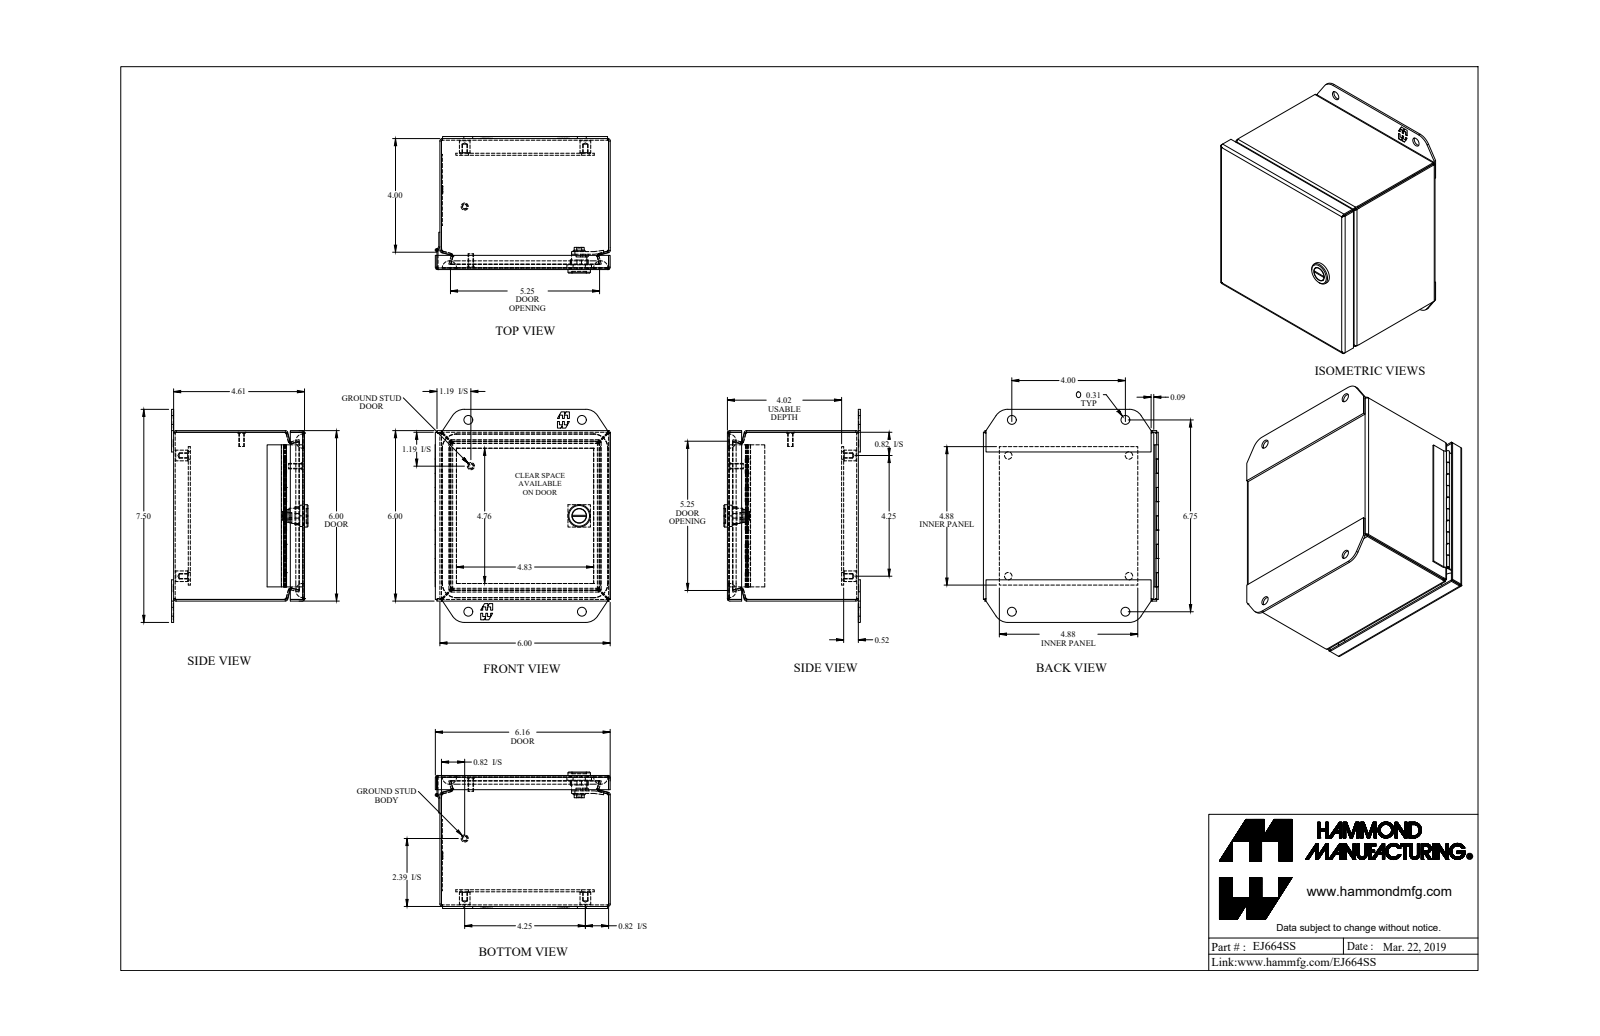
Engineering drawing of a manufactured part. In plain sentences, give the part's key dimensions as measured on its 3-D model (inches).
The part is named "EJ664SS_Default". Its 3-D file was written by "SolidWorks 2019 (CONFIG_CONTROL_DESIGN)". It is 16 solids with 624 faces: 354 planar, 174 cylindrical and 96 other. Overall it measures 7.5 by 6.165 by 4.805 inches. Its volume is 16.45 cubic inches and its surface area 540.5 square inches. Round holes: 4 of diameter 0.156, 4 of diameter 0.265, 4 of diameter 0.313, 1 of diameter 0.05, 1 of diameter 0.516. Round bosses or shafts: 4 of diameter 0.375, 2 of diameter 0.25, 2 of diameter 0.19, 1 of diameter 0.788, 1 of diameter 0.535, 1 of diameter 0.496, 1 of diameter 0.435, 1 of diameter 0.1. Partial cylindrical surfaces (rounded edges, fillets, slot ends): 16 of radius 0.029, 16 of radius 0.086, 12 of radius 0.281, 4 of radius 0.25, 4 of radius 0.499, 4 of radius 0.5, 2 of radius 0.06, 1 of radius 0.03. The main face-to-face distances are 0.057, 5.943, 4.554, 5.886, 6, 0.072, 0.589, 4.611, 4.497, 4.094. The hole center spacings are 1.257, 5.502, 2.136, 3.376, 4, 4.25, 4.25, 4.31.
